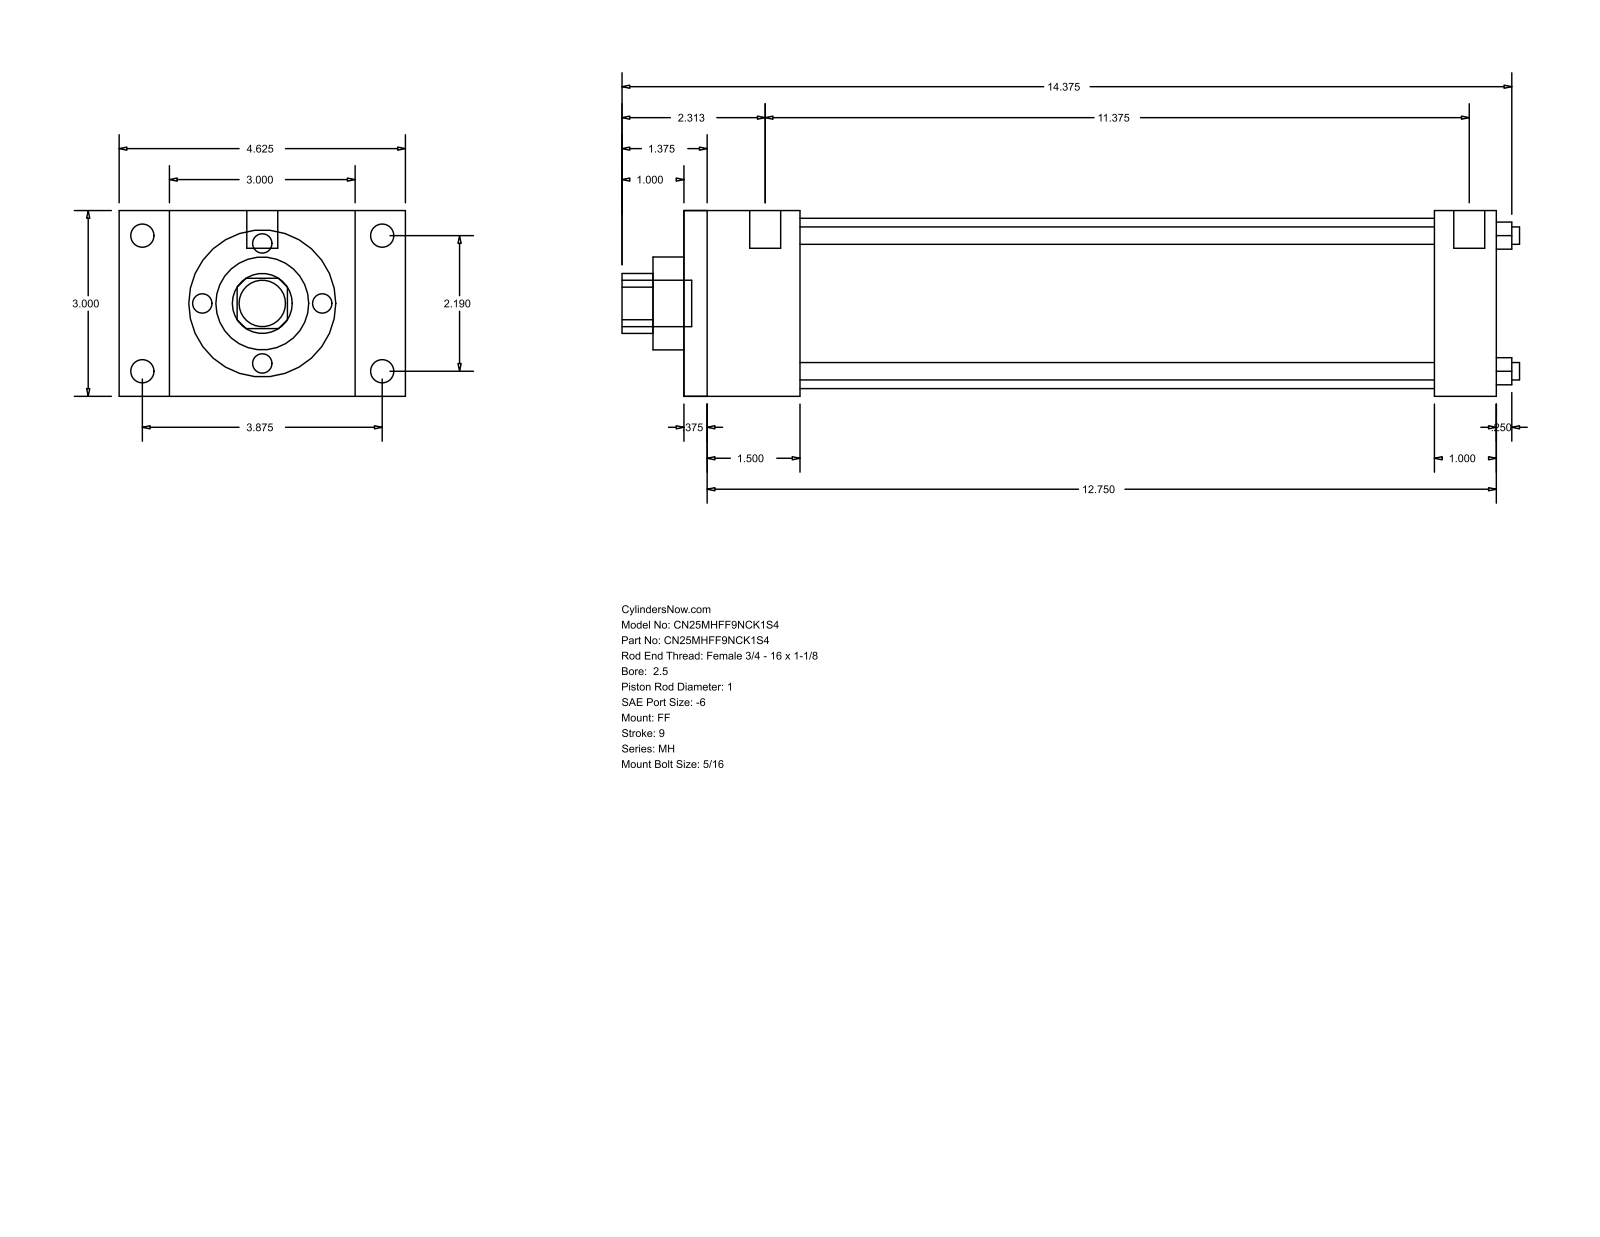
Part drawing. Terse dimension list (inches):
name: MH_FF__0250_1
written by: GSSL Pune (CONFIG_CONTROL_DESIGN)
unit: in
bodies: 0 solids, 92 faces (64 planar, 28 cylindrical, 0 other)
size: 14.5 × 4.625 × 3
holes: 4× ⌀0.281, 1× ⌀1, 1× ⌀1.5, 1× ⌀2.75
bosses: 4× ⌀0.375, 4× ⌀0.219, 2× ⌀0.5, 1× ⌀0.75
rounds: 1× R0.484
face distances: 3, 13.125, 12.75, 0.375, 1, 1.875, 12.125, 1.5, 11.75, 10.25
hole spacings: 1.548, 2.19, 3.097
